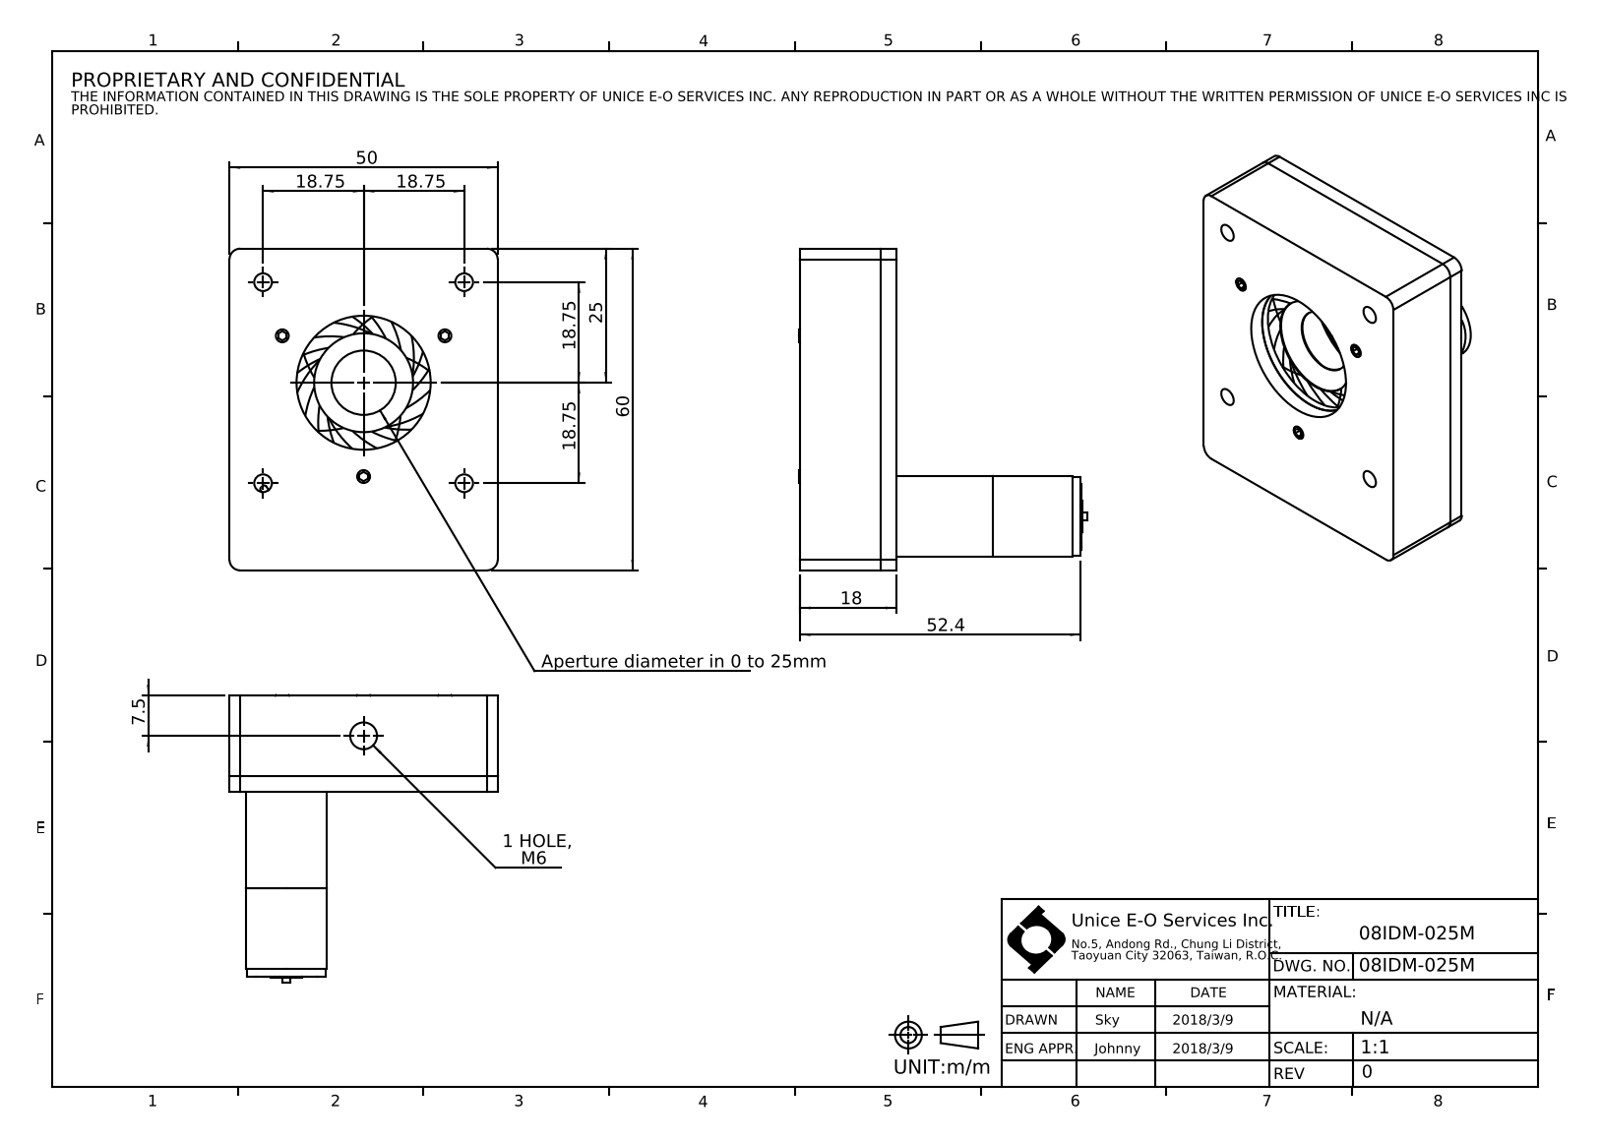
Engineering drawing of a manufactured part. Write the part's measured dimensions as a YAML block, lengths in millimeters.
part_name: "08IDM-025M"
step_written_by: "SolidWorks 2016 (AUTOMOTIVE_DESIGN)"
units: millimeters
bodies: {solids: 0, faces: 218, planar: 127, cylindrical: 75, other: 16}
overall_size: [60, 53.7, 50]
round_holes:
  - {diameter: 3.3, count: 4}
  - {diameter: 4.4, count: 4}
  - {diameter: 1.7, count: 1}
  - {diameter: 3, count: 1}
  - {diameter: 5, count: 1}
  - {diameter: 12, count: 1}
  - {diameter: 18.44, count: 1}
  - {diameter: 25, count: 1}
  - {diameter: 30, count: 1}
round_bosses_or_shafts:
  - {diameter: 1.8, count: 6}
  - {diameter: 15, count: 1}
  - {diameter: 14.8, count: 1}
  - {diameter: 6, count: 1}
  - {diameter: 1.6, count: 1}
  - {diameter: 1.5, count: 1}
partial_cylinders:
  - {radius: 2, count: 4}
face_to_face_distances: [18, 50, 3, 15, 60, 15.1, 12.1, 2.9, 6.8, 11.2]
hole_center_spacings: [26.52, 37.5, 41.42, 5.3, 14.25, 31.82, 39.53, 43.48]
